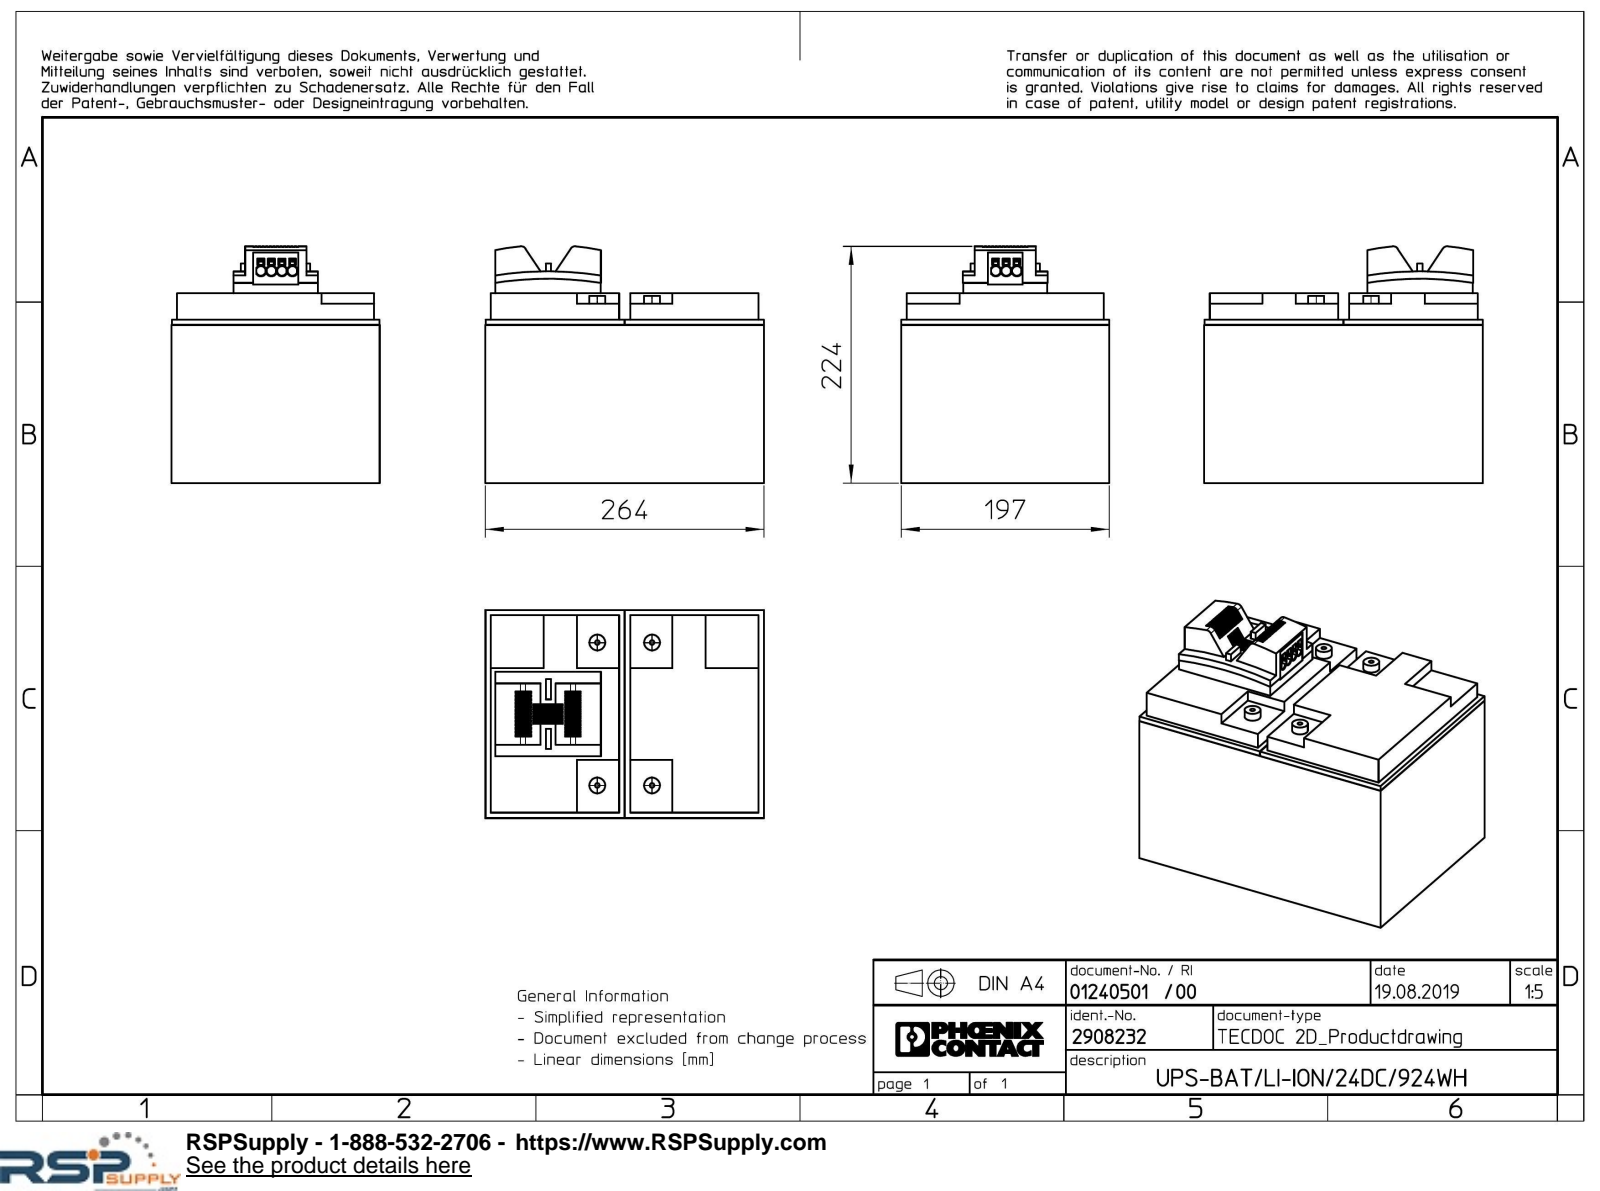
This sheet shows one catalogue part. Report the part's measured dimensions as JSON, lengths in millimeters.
{"part_name": "UPS_BAT_LI_ION_24DC_924WH-select", "step_written_by": "Creo Elements/Direct Modeling 20.1A 29-Sep-2018 (C) Parametric Technology GmbH (AUTOMOTIVE_DESIGN)", "units": "millimeters", "bodies": {"solids": 1, "faces": 578, "planar": 385, "cylindrical": 179, "other": 14}, "overall_size": [264, 223.88, 197], "volume_mm3": 9291000, "surface_area_mm2": 301906, "round_holes": [[4.5, 4]], "round_bosses_or_shafts": [[15, 4]], "partial_cylinders_radius": [[4.6, 7], [2.9, 2], [3.8, 2], [4.7, 2], [5, 2], [325, 2], [250.4, 1], [252.5, 1]], "face_to_face_distances": [197, 264, 179.5, 5.2, 169.5, 10, 191.8, 132, 258.8, 126.8], "hole_center_spacings": [51.9, 135.1, 144.73]}
